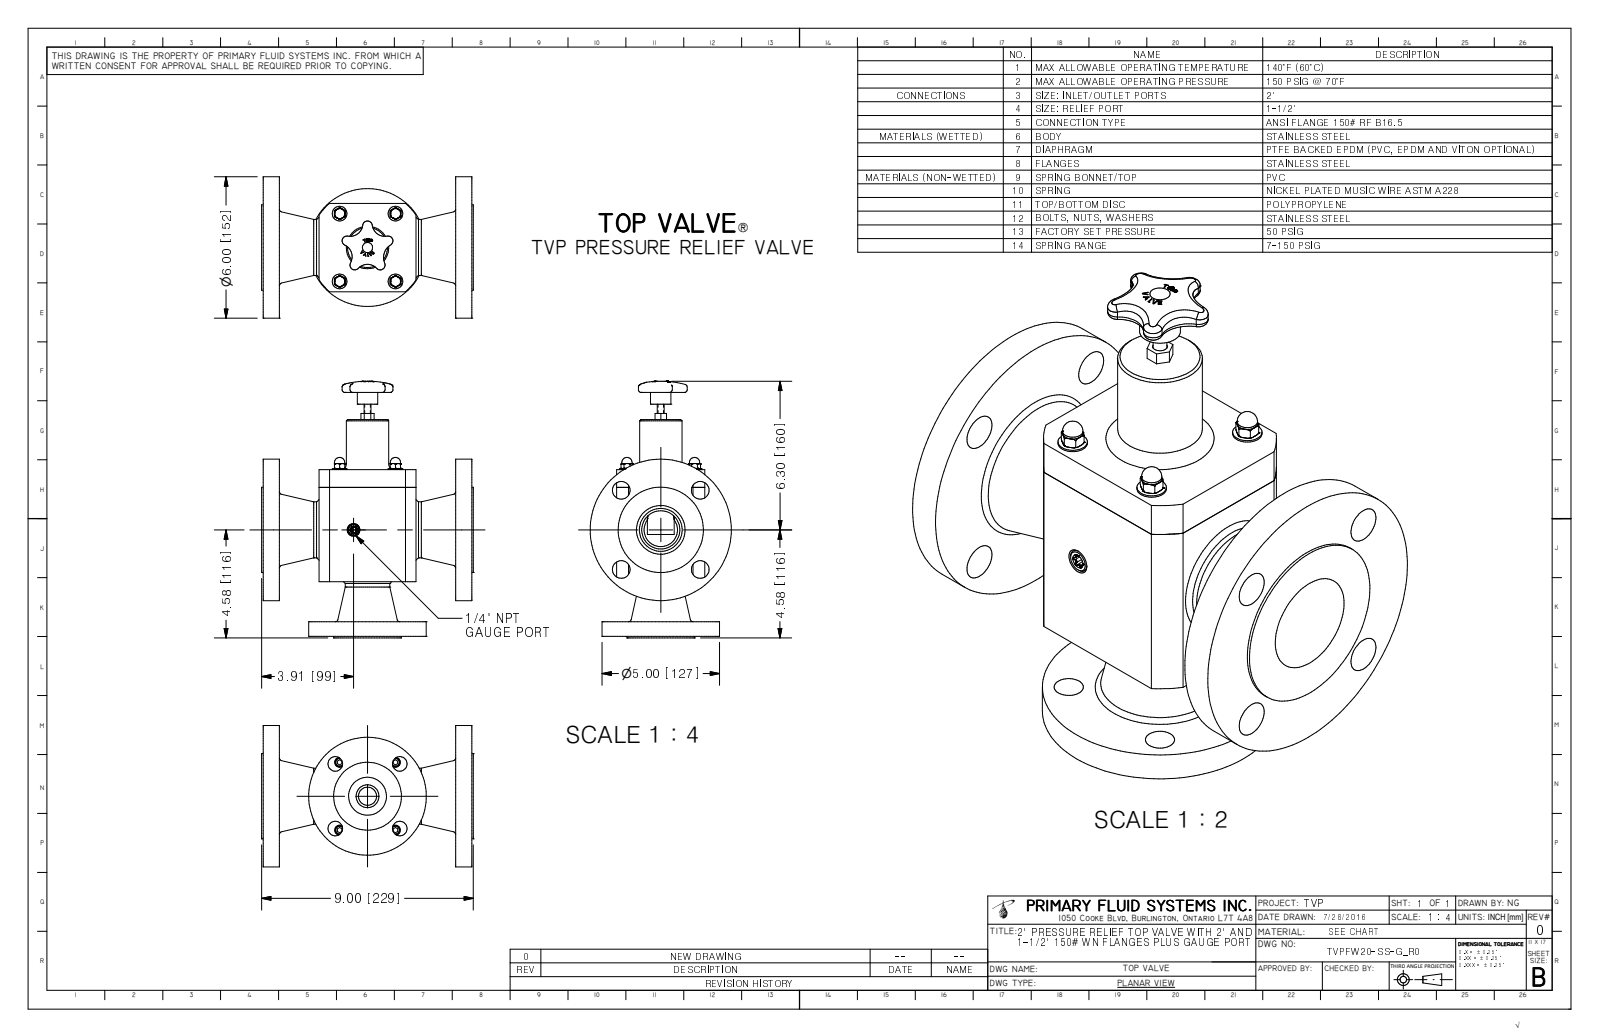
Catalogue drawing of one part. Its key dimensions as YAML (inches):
part_name: "TVPFW20-SS-G_R0"
step_written_by: "Autodesk Inventor 2009 (AUTOMOTIVE_DESIGN)"
units: inches
bodies: {solids: 1, faces: 398, planar: 162, cylindrical: 73, other: 163}
overall_size: [10.88, 9, 6]
volume: 130.1
surface_area: 383.7
round_holes:
  - {diameter: 0.175, count: 4}
  - {diameter: 0.62, count: 4}
  - {diameter: 0.75, count: 4}
  - {diameter: 1.61, count: 1}
  - {diameter: 2.067, count: 1}
round_bosses_or_shafts:
  - {diameter: 0.625, count: 4}
  - {diameter: 0.433, count: 4}
  - {diameter: 0.375, count: 4}
  - {diameter: 6, count: 1}
  - {diameter: 5, count: 1}
  - {diameter: 3.62, count: 1}
  - {diameter: 2.88, count: 1}
  - {diameter: 2.375, count: 1}
partial_cylinders:
  - {radius: 0.027, count: 6}
  - {radius: 0.085, count: 5}
  - {radius: 0.205, count: 5}
  - {radius: 0.536, count: 4}
  - {radius: 0.656, count: 4}
  - {radius: 0.625, count: 1}
  - {radius: 0.745, count: 1}
  - {radius: 2.475, count: 1}
face_to_face_distances: [0.69, 8.185, 0.063, 7.495, 8.875, 2.375, 6.5, 1.685, 5.81, 3.75]
hole_center_spacings: [1.94, 2.375, 2.56, 2.743, 3.359, 0.196, 0.196, 1.864]
